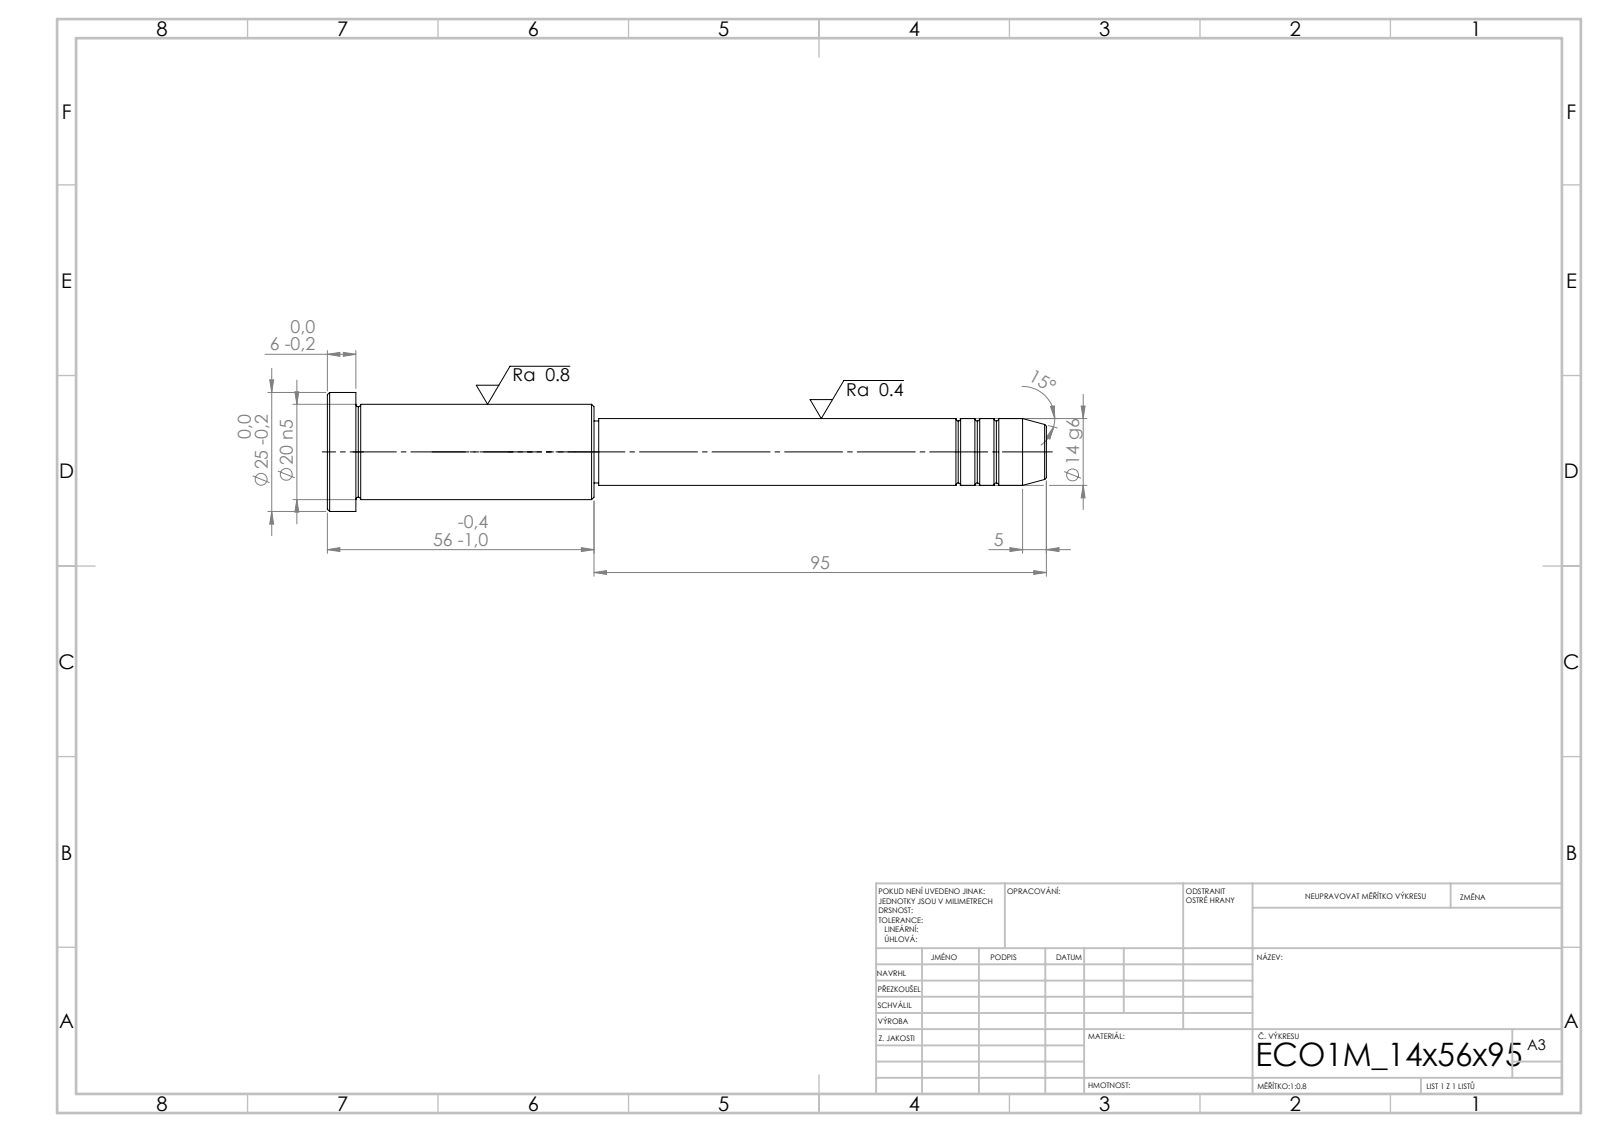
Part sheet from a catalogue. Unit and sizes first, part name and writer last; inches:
Units: inches
Overall size (bounding box): 5.945 × 0.984 × 0.984
Round bosses / shafts (diameter × count): ⌀0.984 ×1, ⌀0.787 ×1, ⌀0.551 ×1, ⌀0.512 ×1
Main face-to-face distances: 0.236, 1.969, 2.205, 3.74, 5.709, 5.945, 3.701, 0.039, 2.008, 2.244
Volume: 2.015 in³ · Surface area: 13.64 in²
Bodies: 1 solid, 43 faces (5 planar, 14 cylindrical, 24 other)
STEP written by: SolidWorks 2019 (CONFIG_CONTROL_DESIGN)
